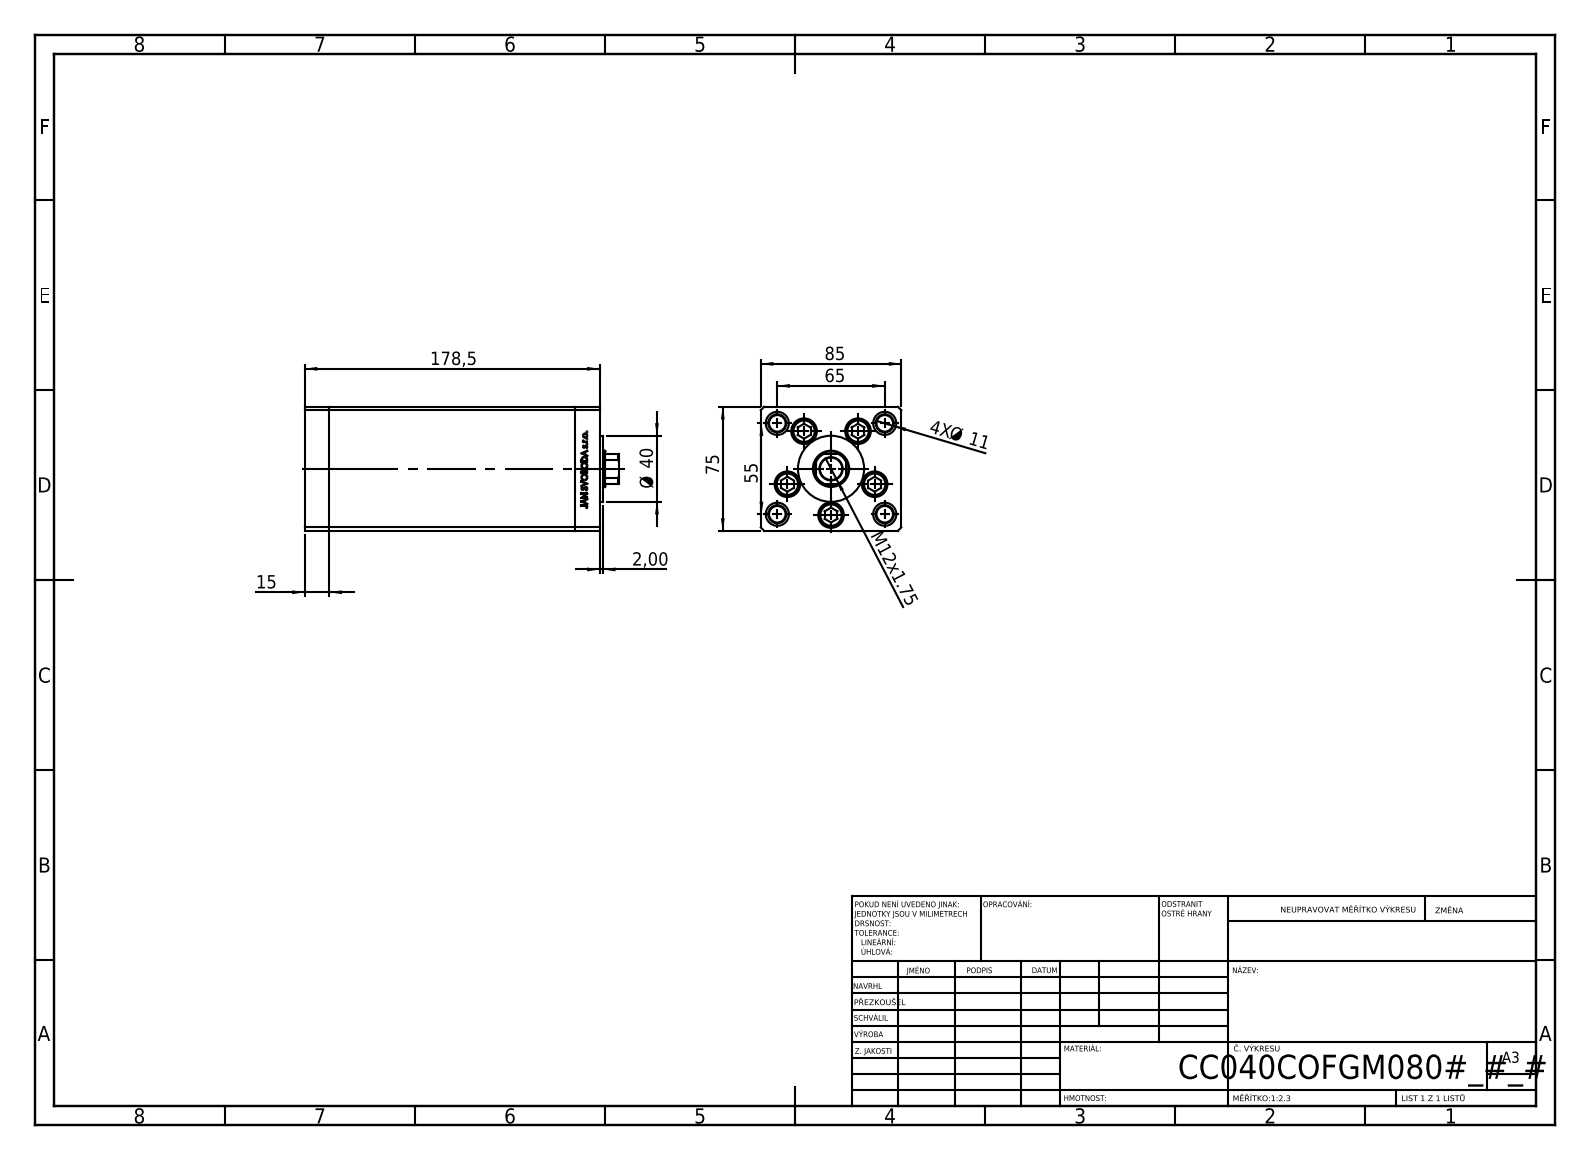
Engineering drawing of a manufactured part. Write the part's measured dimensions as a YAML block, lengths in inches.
part_name: "V220C_C MIDDLE; V220C BACK_C; V220C FRONT; V220C_VC_C (+1 more)"
step_written_by: "SolidWorks 2019 (CONFIG_CONTROL_DESIGN)"
units: inches
bodies: {solids: 13, faces: 1159, planar: 538, cylindrical: 159, other: 462}
overall_size: [7.48, 3.346, 2.953]
volume: 57.91
surface_area: 277.8
round_holes:
  - {diameter: 0.433, count: 9}
  - {diameter: 0.61, count: 5}
  - {diameter: 0.394, count: 4}
  - {diameter: 0.551, count: 4}
  - {diameter: 0.531, count: 1}
  - {diameter: 0.571, count: 1}
  - {diameter: 0.866, count: 1}
round_bosses_or_shafts:
  - {diameter: 0.315, count: 5}
  - {diameter: 0.571, count: 4}
  - {diameter: 1.575, count: 1}
partial_cylinders:
  - {radius: 0.037, count: 2}
  - {radius: 0.413, count: 1}
face_to_face_distances: [3.346, 2.953, 0.591, 5.846, 6.437, 0.413, 7.028, 1.348, 5.679, 5.089]
hole_center_spacings: [1.102, 1.676, 0.664, 0.755, 1.273, 1.28, 1.324, 1.47]
